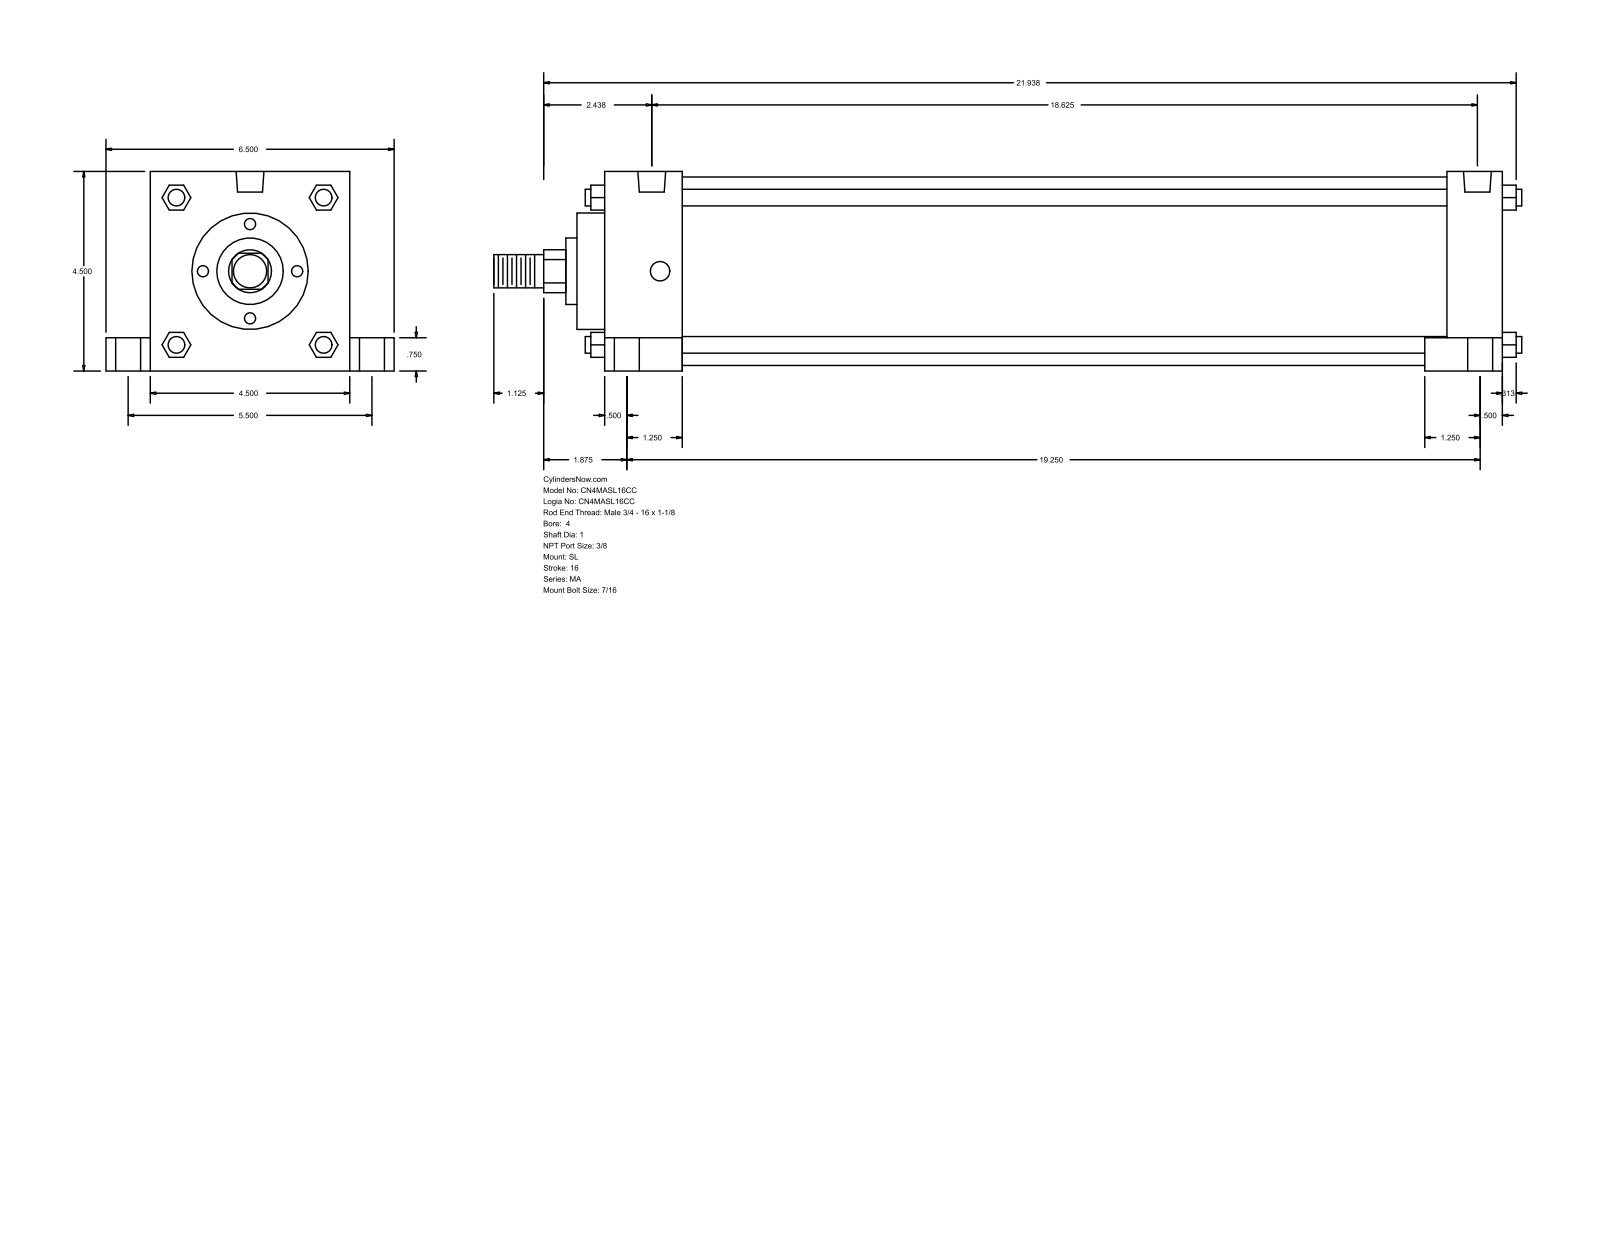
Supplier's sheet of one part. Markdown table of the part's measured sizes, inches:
| quantity | value |
| --- | --- |
| part name | MA_SL__0400_1 |
| STEP written by | GSSL Pune (CONFIG_CONTROL_DESIGN) |
| units | inches |
| bodies | 0 solids, 150 faces (113 planar, 37 cylindrical, 0 other) |
| overall size | 23.187 × 6.5 × 4.5 |
| round holes (diameter × count) | 0.437 × 4, 0.563 × 4, 0.813 × 4, 0.627 × 2 |
| round bosses / shafts (diameter × count) | 0.375 × 4, 4.25 × 1, 2.625 × 1, 1.5 × 1, 1 × 1, 0.75 × 1 |
| partial cylindrical surfaces (radius × count) | 0.484 × 1 |
| main face-to-face distances | 4.5, 20.25, 1.75, 18.5, 19, 17.25, 1.25, 1, 5.5, 20.875 |
| hole center spacings | 0.187, 2.751, 2.761, 2.807, 2.85, 5.5, 18.25, 18.438 |
